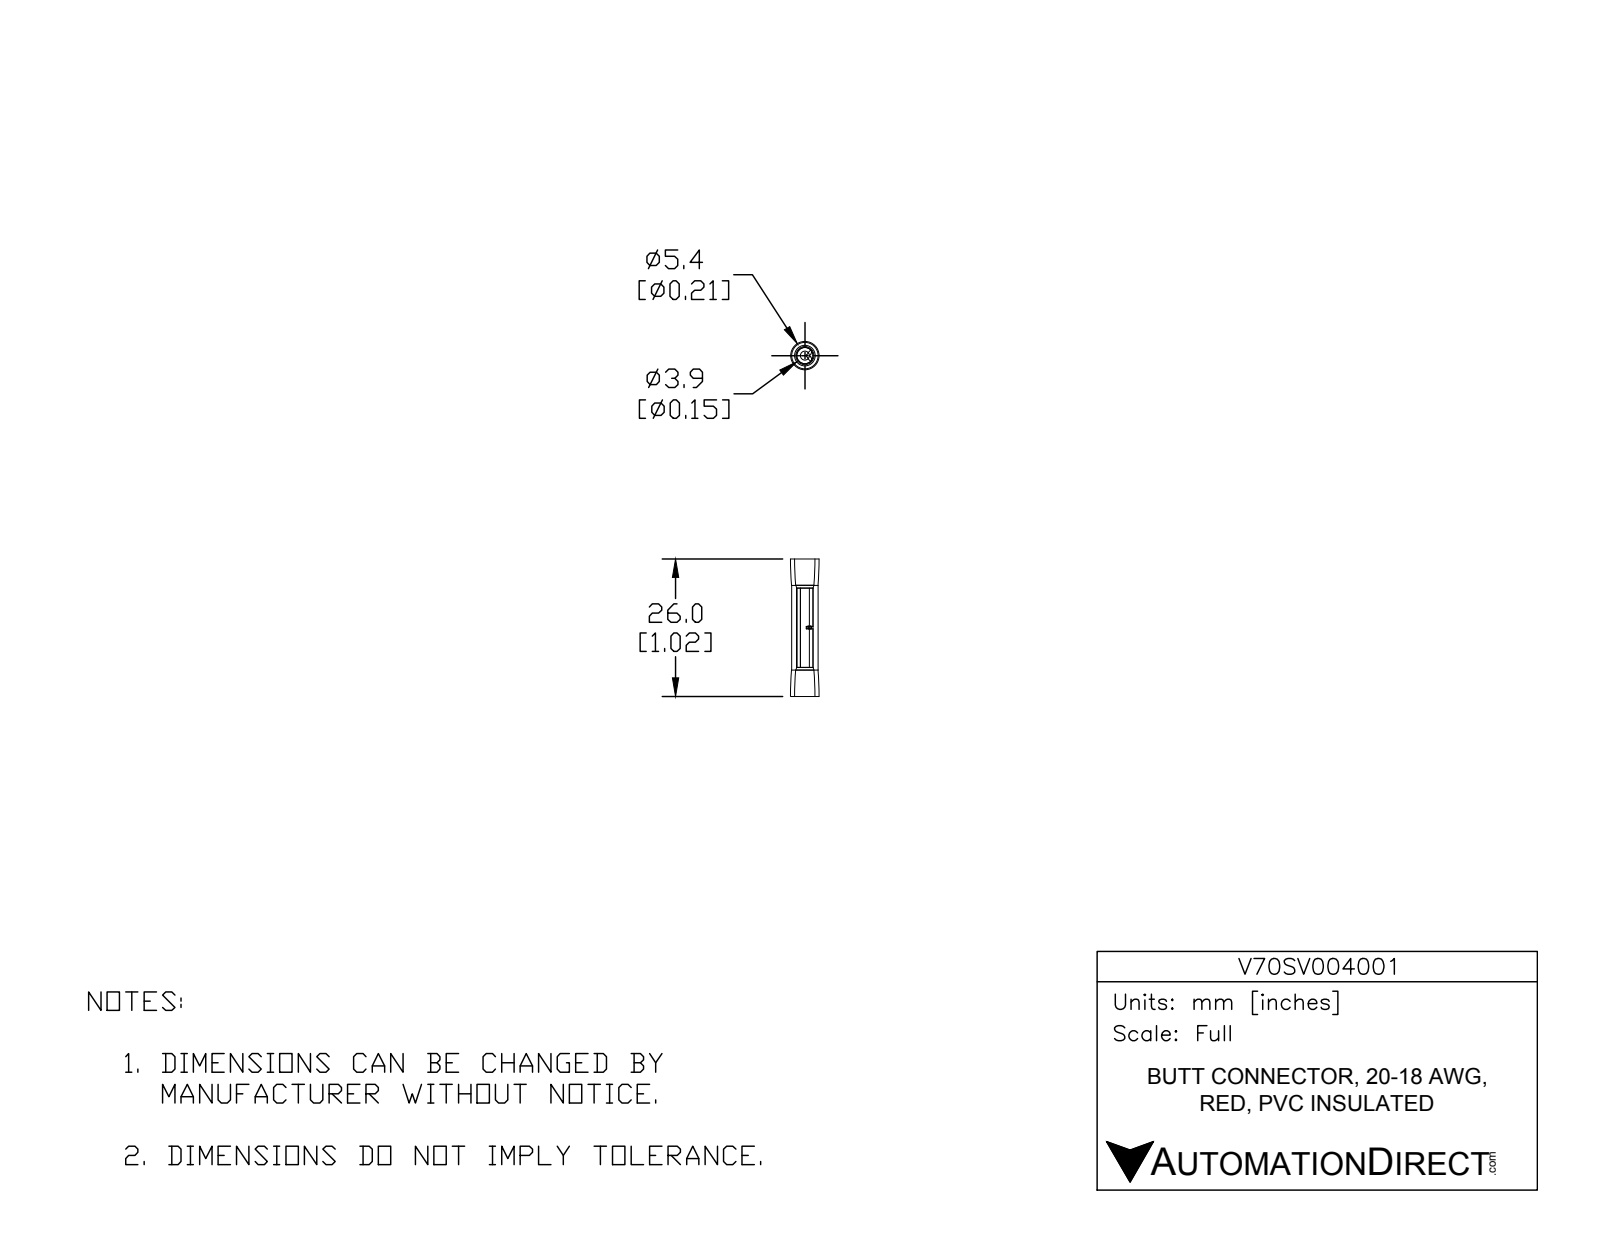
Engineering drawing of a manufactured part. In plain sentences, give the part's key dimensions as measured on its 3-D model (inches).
The part is named "V70SV004001". Its 3-D file was written by "SolidWorks 2017 (AUTOMOTIVE_DESIGN)". It is 2 solids with 41 faces: 18 planar, 11 cylindrical and 12 other. Overall it measures 1.024 by 0.213 by 0.213 inches. Its volume is 0.023 cubic inches and its surface area 1.51 square inches. Round holes: 1 of diameter 0.067, 1 of diameter 0.122. Round bosses or shafts: 1 of diameter 0.197. Partial cylindrical surfaces (rounded edges, fillets, slot ends): 2 of radius 0.004, 2 of radius 0.024, 1 of radius 0.01. The main face-to-face distances are 1.024, 0.217, 0.807, 0.591, 0.503, 0.521, 0.286, 0.304, 0.503, 0.52.
